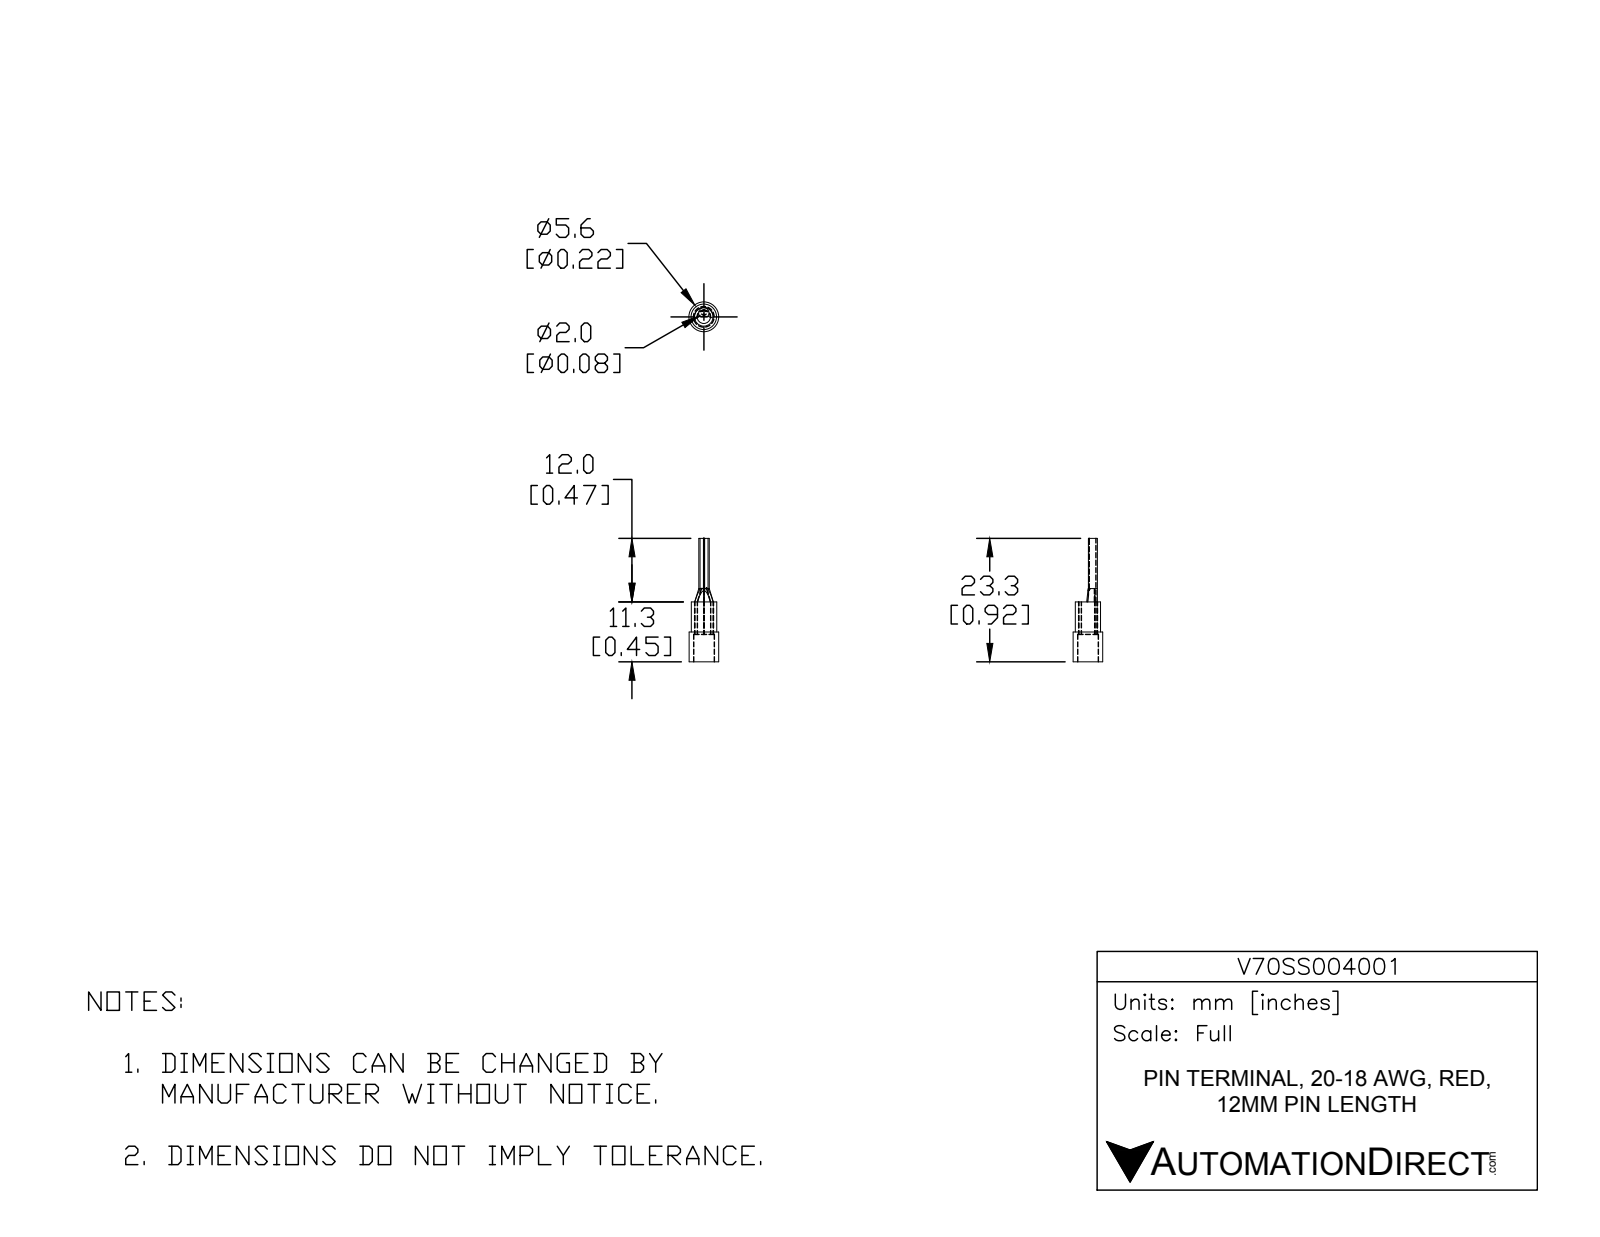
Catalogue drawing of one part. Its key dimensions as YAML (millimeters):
part_name: "V70SS004001"
step_written_by: "SolidWorks 2017 (AUTOMOTIVE_DESIGN)"
units: millimeters
bodies: {solids: 3, faces: 42, planar: 20, cylindrical: 16, other: 6}
overall_size: [23.34, 5.6, 5.6]
volume: 181
surface_area: 592
round_holes:
  - {diameter: 2.52, count: 1}
  - {diameter: 3.52, count: 1}
  - {diameter: 3.9, count: 1}
round_bosses_or_shafts:
  - {diameter: 5.6, count: 1}
  - {diameter: 4.8, count: 1}
partial_cylinders:
  - {radius: 0.1, count: 2}
  - {radius: 1, count: 1}
face_to_face_distances: [11.34, 5.2, 6.14, 5.64, 0.44, 5.7, 23.34, 18.14, 17.7, 12]
